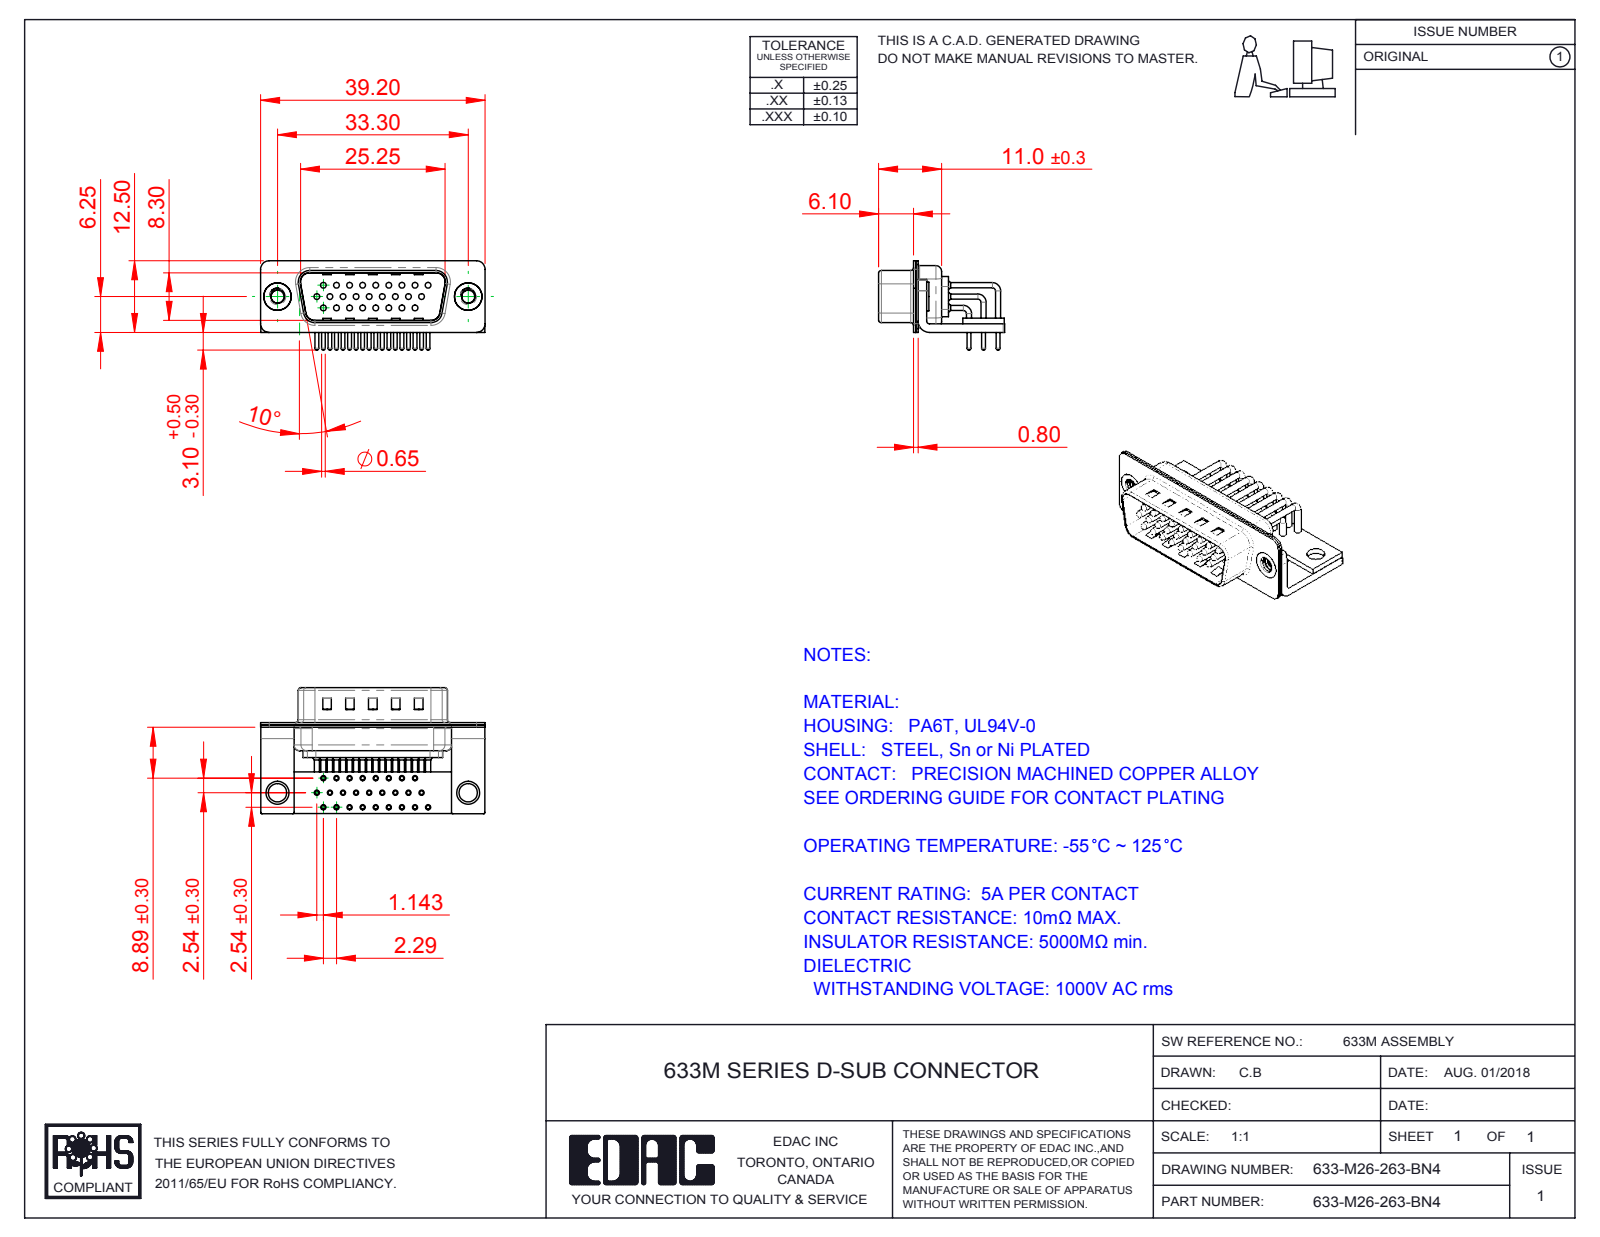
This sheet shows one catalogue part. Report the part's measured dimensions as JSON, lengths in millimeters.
{"part_name": "633M Stabilizer Board_26 Contacts; 633M Shell Rear_26 Contacts; 633-M26-263-BN4; 633M Stabilizer Bracket (+6 more)", "step_written_by": "SolidWorks 2016 (CONFIG_CONTROL_DESIGN)", "units": "millimeters", "bodies": {"solids": 34, "faces": 3302, "planar": 1829, "cylindrical": 1143, "other": 330}, "overall_size": [39.2, 22, 15.6], "volume_mm3": 2620, "surface_area_mm2": 7989, "round_holes": [[0.9, 26], [1, 26], [1.7, 26], [2, 26], [2.26, 2], [3.2, 2], [4, 2], [4.8, 2]], "round_bosses_or_shafts": [[1.5, 26], [0.9, 26], [0.65, 26], [5, 2], [4.9, 2]], "partial_cylinders_radius": [[1.01, 26], [0.25, 16], [1.5, 16], [2, 13], [0.5, 9], [1.6, 8], [0.6, 4], [0.65, 4]], "face_to_face_distances": [0.4, 1.5, 0.85, 0.8, 1.25, 1, 1.9, 10.4, 9.55, 2.5], "hole_center_spacings": [4.57, 2.29, 2.28, 3.96, 6.86, 4.27, 6.05, 2.78]}
